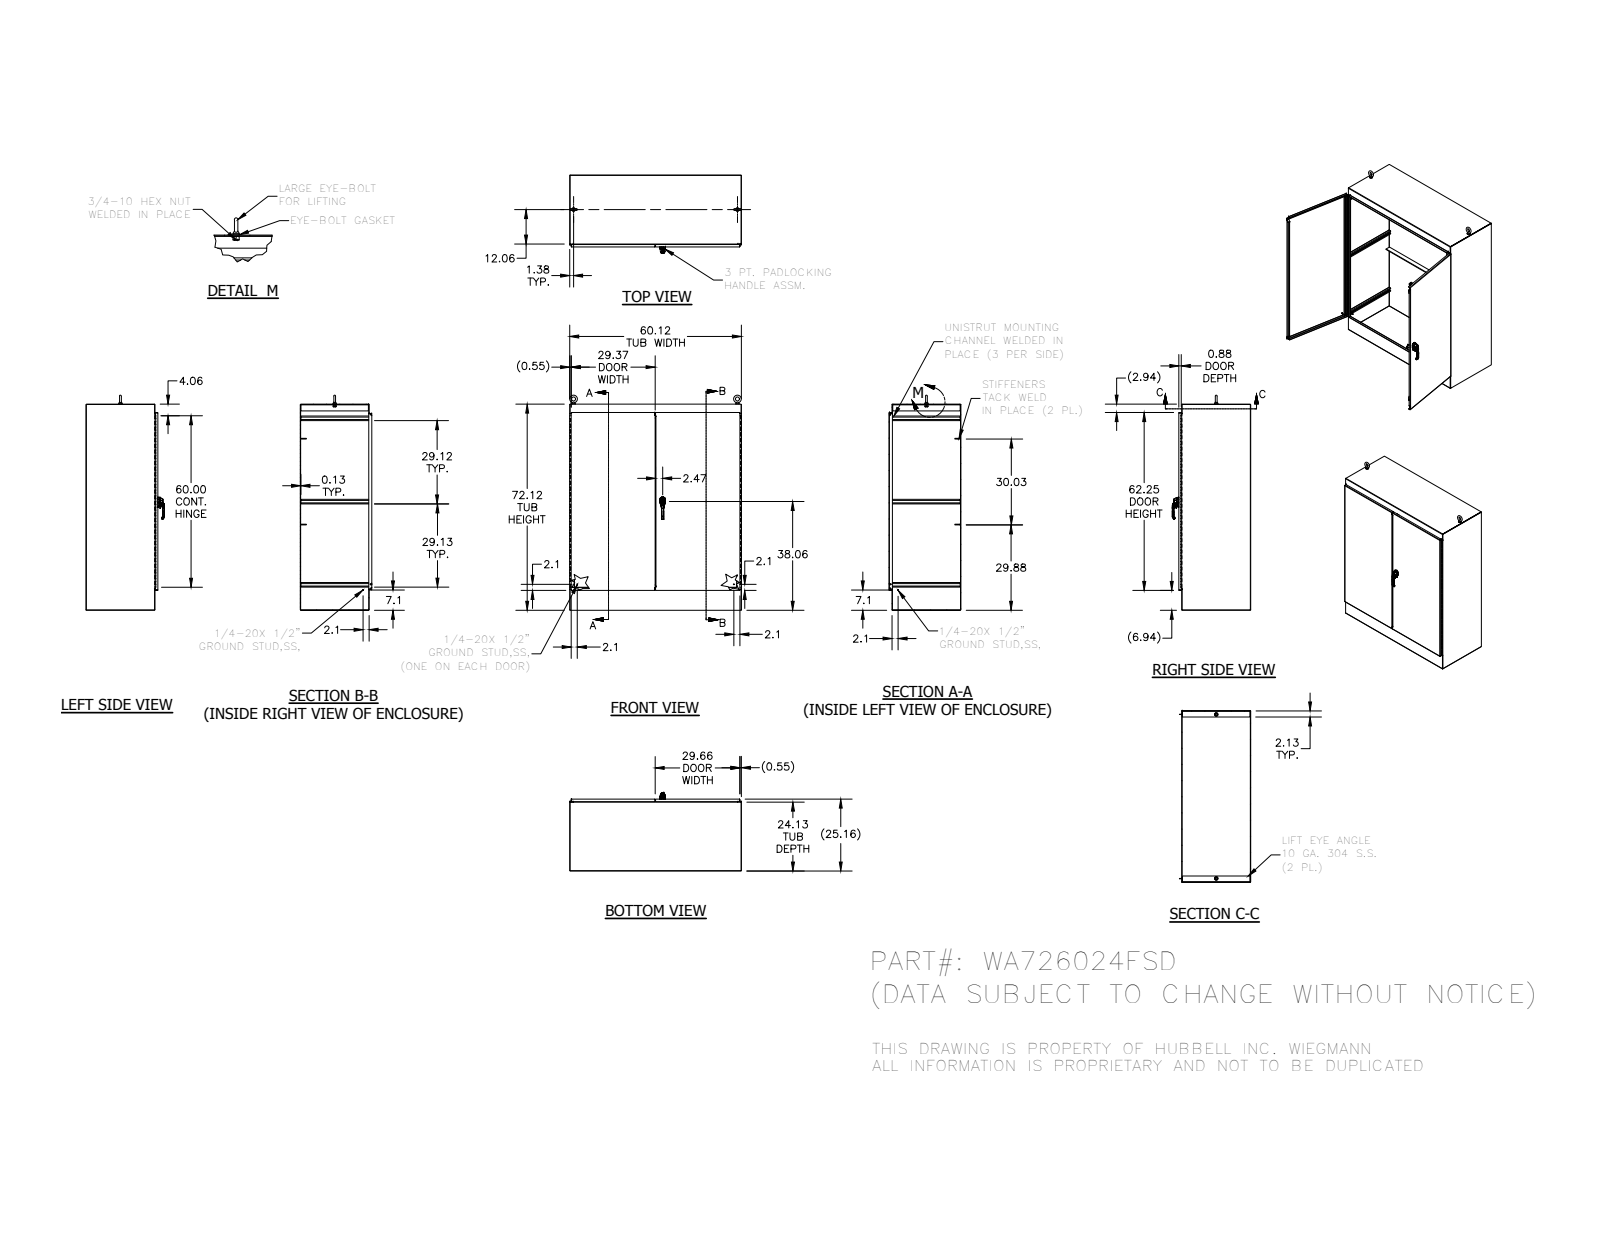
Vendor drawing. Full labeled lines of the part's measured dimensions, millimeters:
Part name (STEP PRODUCT): FUN00103; HFW3025; 316298; 349132 (+8 more)
STEP written by: Autodesk Inventor 2014 (AUTOMOTIVE_DESIGN)
Units: millimetres
Bodies: 66 solids, 3780 faces (1777 planar, 1263 cylindrical, 740 other)
Overall size (bounding box): 1911.29 × 1527.54 × 696.76
Volume: 35 970 000 mm³ · Surface area: 22 710 000 mm²
Round holes (diameter × count): ⌀7.02 ×8, ⌀5.08 ×4, ⌀5.4 ×3, ⌀6 ×3, ⌀7.11 ×3, ⌀3.17 ×2, ⌀6.13 ×2, ⌀6.35 ×2, ⌀6.41 ×2, ⌀10.16 ×2, ⌀10.33 ×2, ⌀10.5 ×2
Round bosses / shafts (diameter × count): ⌀6.35 ×5, ⌀8.56 ×3, ⌀31.75 ×2, ⌀28.45 ×2, ⌀25.4 ×2, ⌀19.05 ×2, ⌀14.29 ×2, ⌀13.37 ×2
Partial cylindrical surfaces — rounded edges, fillets, slot ends (radius × count): R0.5 ×164, R0.3 ×84, R0.79 ×24, R3.97 ×21, R0.47 ×19, R0.25 ×16, R2 ×15, R1.27 ×14
Main face-to-face distances: 3.18, 3.17, 635.97, 632.79, 639.14, 635.96, 1524, 1828.8, 1520.82, 1527.18
Hole centre spacings: 6, 6.5, 9.67, 9.69, 9.72, 12.49, 12.5, 19.36
